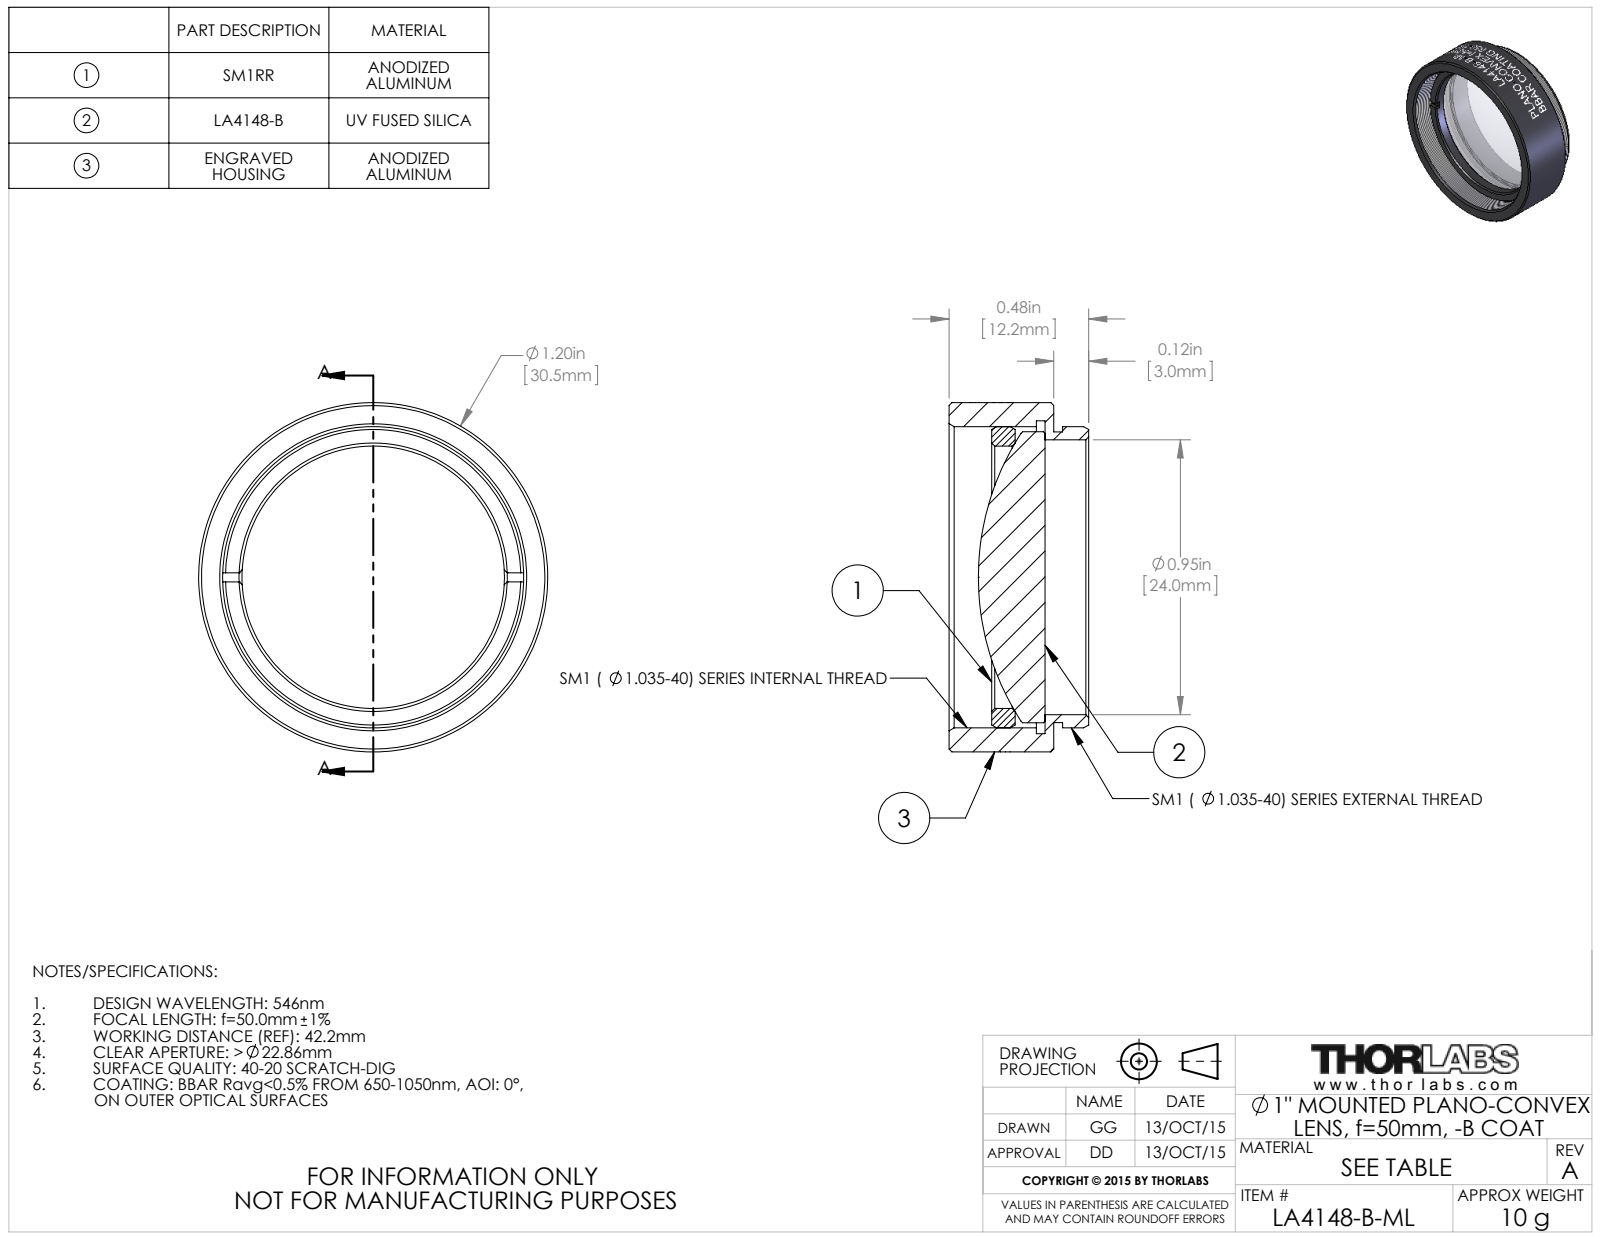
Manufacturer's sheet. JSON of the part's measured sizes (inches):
{"part_name": "TTN039168-E0W", "step_written_by": "SolidWorks 2014 (CONFIG_CONTROL_DESIGN)", "units": "inches", "bodies": {"solids": 3, "faces": 163, "planar": 20, "cylindrical": 115, "other": 28}, "overall_size": [1.2, 1.2, 0.48], "volume_in3": 0.258, "surface_area_in2": 6.953, "round_holes": [[0.902, 1], [0.945, 1], [1.075, 1]], "round_bosses_or_shafts": [[1.2, 1], [1.035, 1], [1, 1], [0.999, 1]], "face_to_face_distances": [0.03, 0.36, 0.33, 0.133, 0.103, 0.227, 0.213, 0.183, 0.08, 0.147]}
